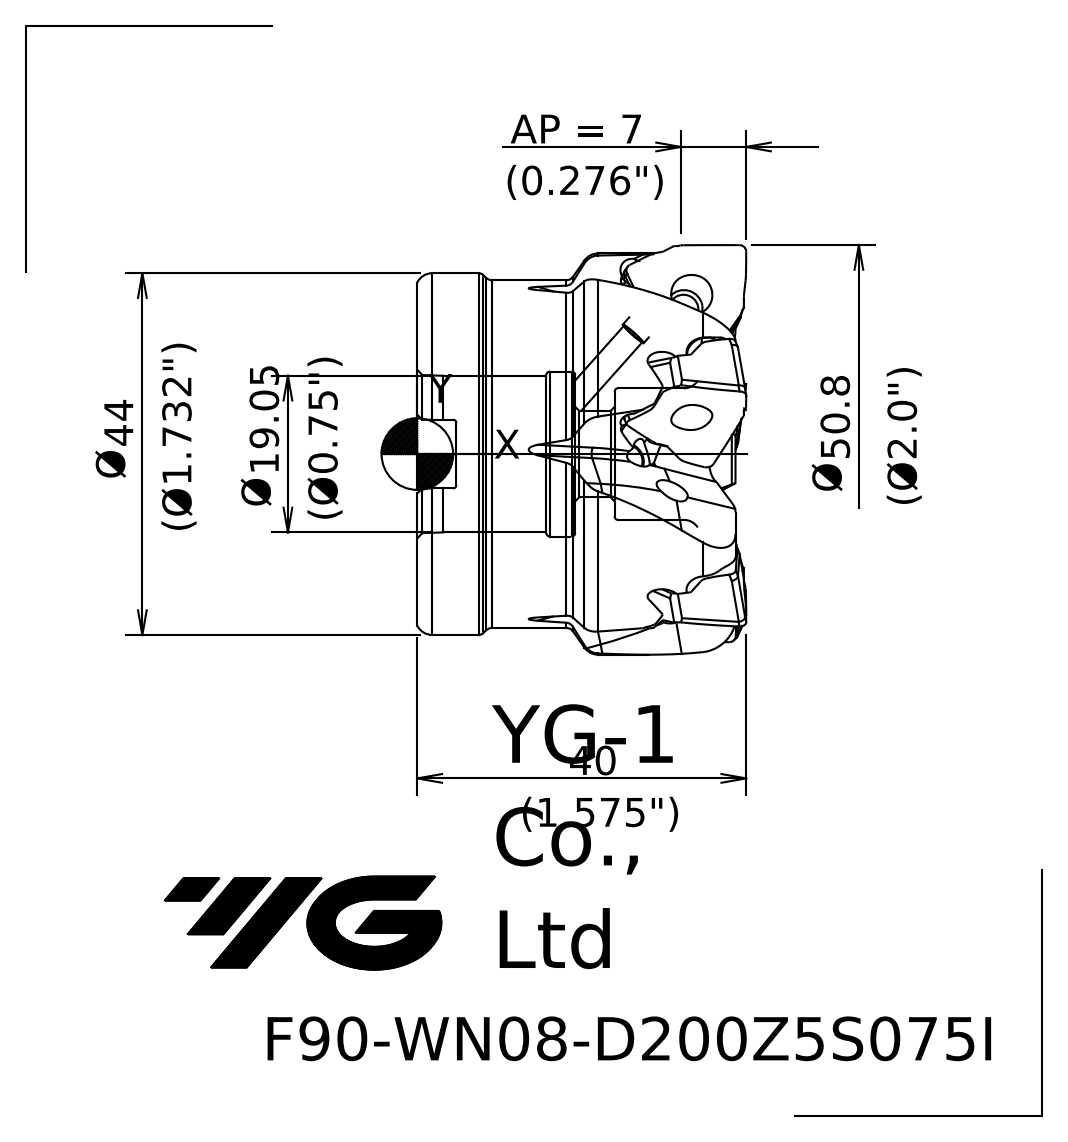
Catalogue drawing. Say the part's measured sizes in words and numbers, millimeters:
The part is named "10223F5CCA8Abcie". Its 3-D file was written by "SIEMENS PLM Software NX 10.0 (AP203_CONFIGURATION_CONTROLLED_3D_DESIGN_OF_MECHANICAL_PARTS_AND_ASSEMBLIES_MIM_LF)". It is 1 solid with 90 faces: 16 planar, 11 cylindrical and 63 other. Overall it measures 50.81 by 50.81 by 40 millimeters. Its volume is 52 086 cubic millimeters and its surface area 16 084 square millimeters. Round holes: 1 of diameter 10.5, 1 of diameter 16, 1 of diameter 19.05, 1 of diameter 20.05. Round bosses or shafts: 1 of diameter 48.8, 1 of diameter 44, 1 of diameter 42.3. Partial cylindrical surfaces (rounded edges, fillets, slot ends): 2 of radius 0.4. The main face-to-face distances are 38.7, 33.95, 4.75, 19.5, 14.45, 19.2, 8.35, 14.7, 4.8, 19.25.
